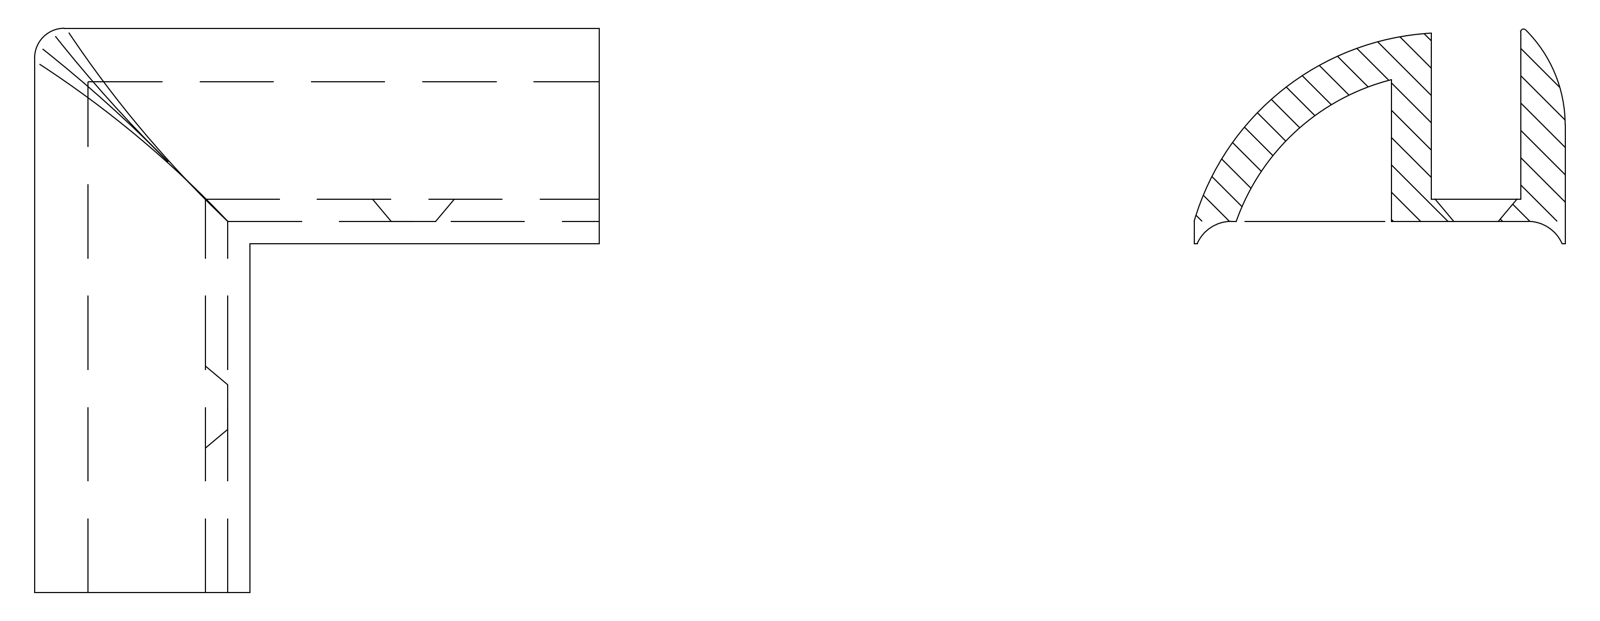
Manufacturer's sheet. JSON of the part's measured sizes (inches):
{"step_written_by": "THINKDESIGN (CONFIG_CONTROL_DESIGN)", "units": "inches", "bodies": {"solids": 1, "faces": 39, "planar": 19, "cylindrical": 14, "other": 6}, "overall_size": [1.488, 1.488, 0.983], "volume_in3": 0.47, "surface_area_in2": 11.17, "partial_cylinders_radius": [[0.098, 4], [0.012, 2], [0.354, 2], [0.591, 2], [0.697, 2], [0.039, 1]], "face_to_face_distances": [0.236, 0.343, 0.106, 0.118, 0.354, 0.461, 0.059, 0.02, 0.984, 1.043]}
